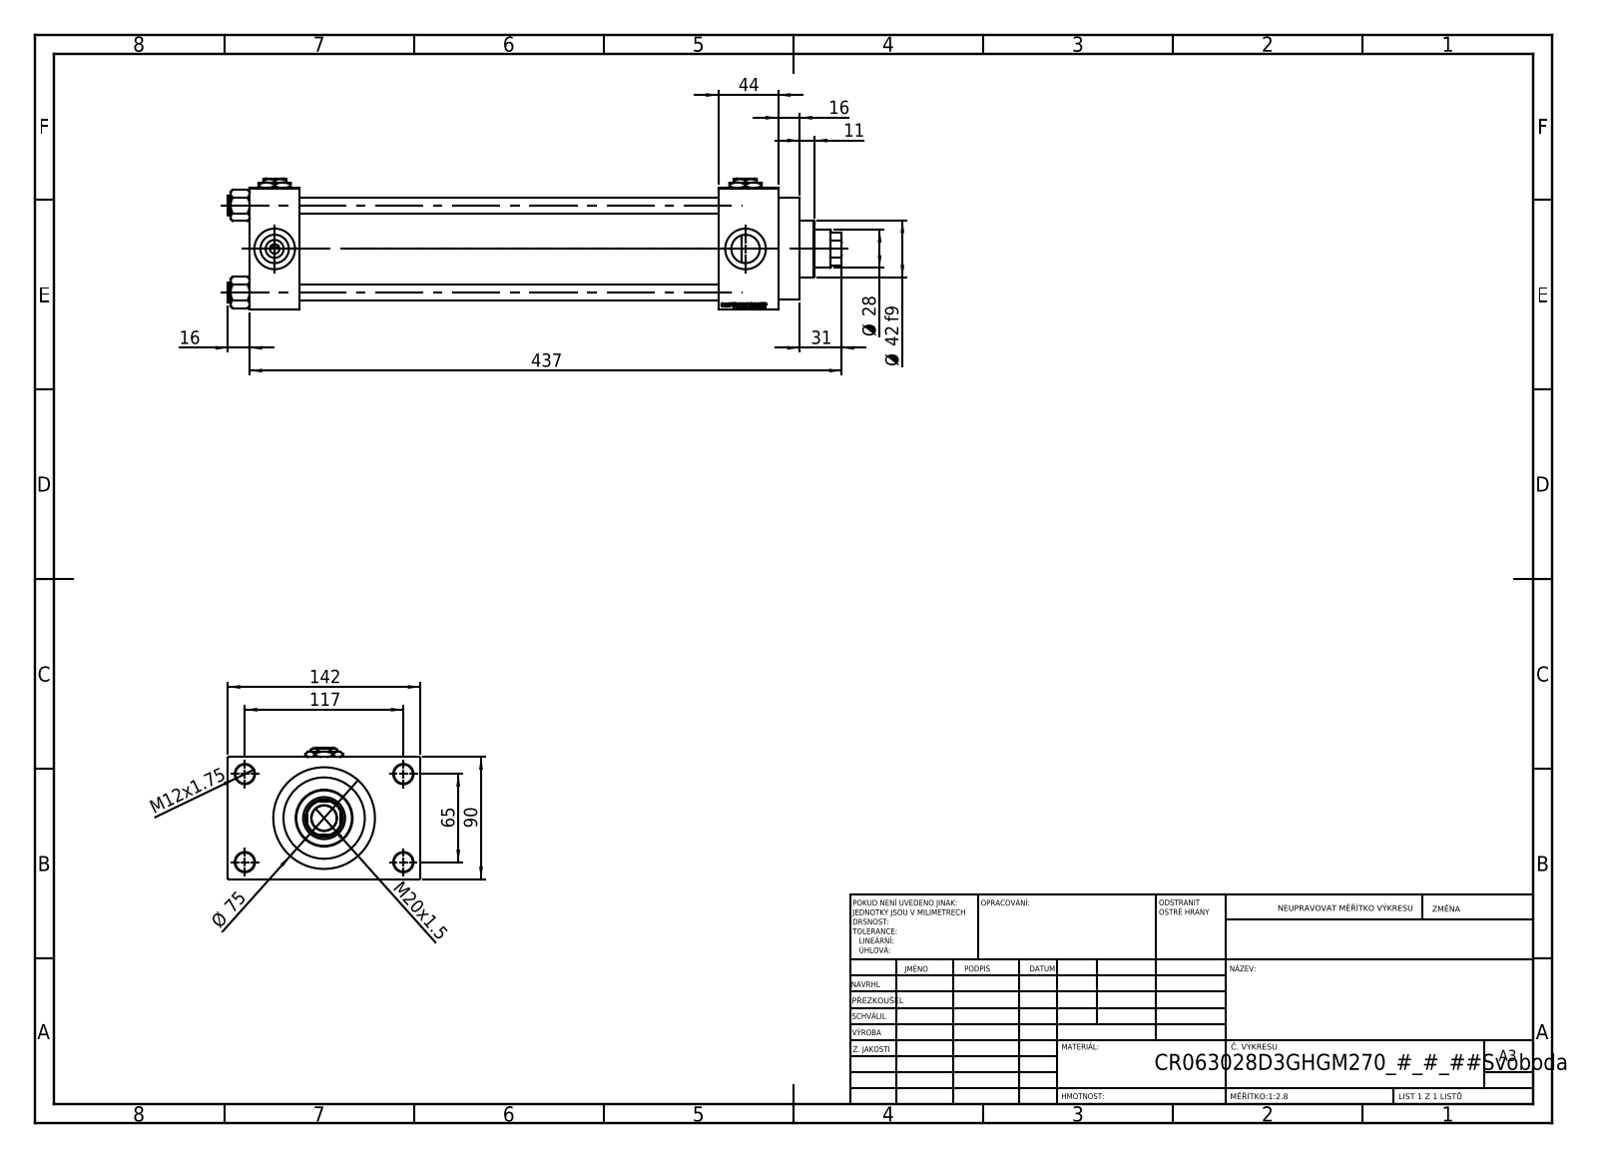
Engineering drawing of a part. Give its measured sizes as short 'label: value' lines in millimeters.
name: NUT_M5_D; V215_VC_A; Zatka_pro_OIL_PORT; V215CR_D_TYCINKA (+2 more)
written by: SolidWorks 2019 (CONFIG_CONTROL_DESIGN)
unit: mm
bodies: 13 solids, 1204 faces (545 planar, 99 cylindrical, 560 other)
size: 453 × 142 × 97
volume: 1 513 000 mm³; area: 368 304 mm²
holes: 4× ⌀12, 4× ⌀14, 4× ⌀20.96, 4× ⌀30, 3× ⌀7, 1× ⌀18.5, 1× ⌀28, 1× ⌀31, 1× ⌀50, 1× ⌀60, 1× ⌀63
bosses: 4× ⌀15, 1× ⌀75, 1× ⌀69, 1× ⌀42
rounds: 1× R13.5
face distances: 90, 309, 37, 346, 353, 390, 44, 26, 116, 16
hole spacings: 26.35, 45.47, 64.3, 66.92, 69.81, 90.65, 111.34, 65
